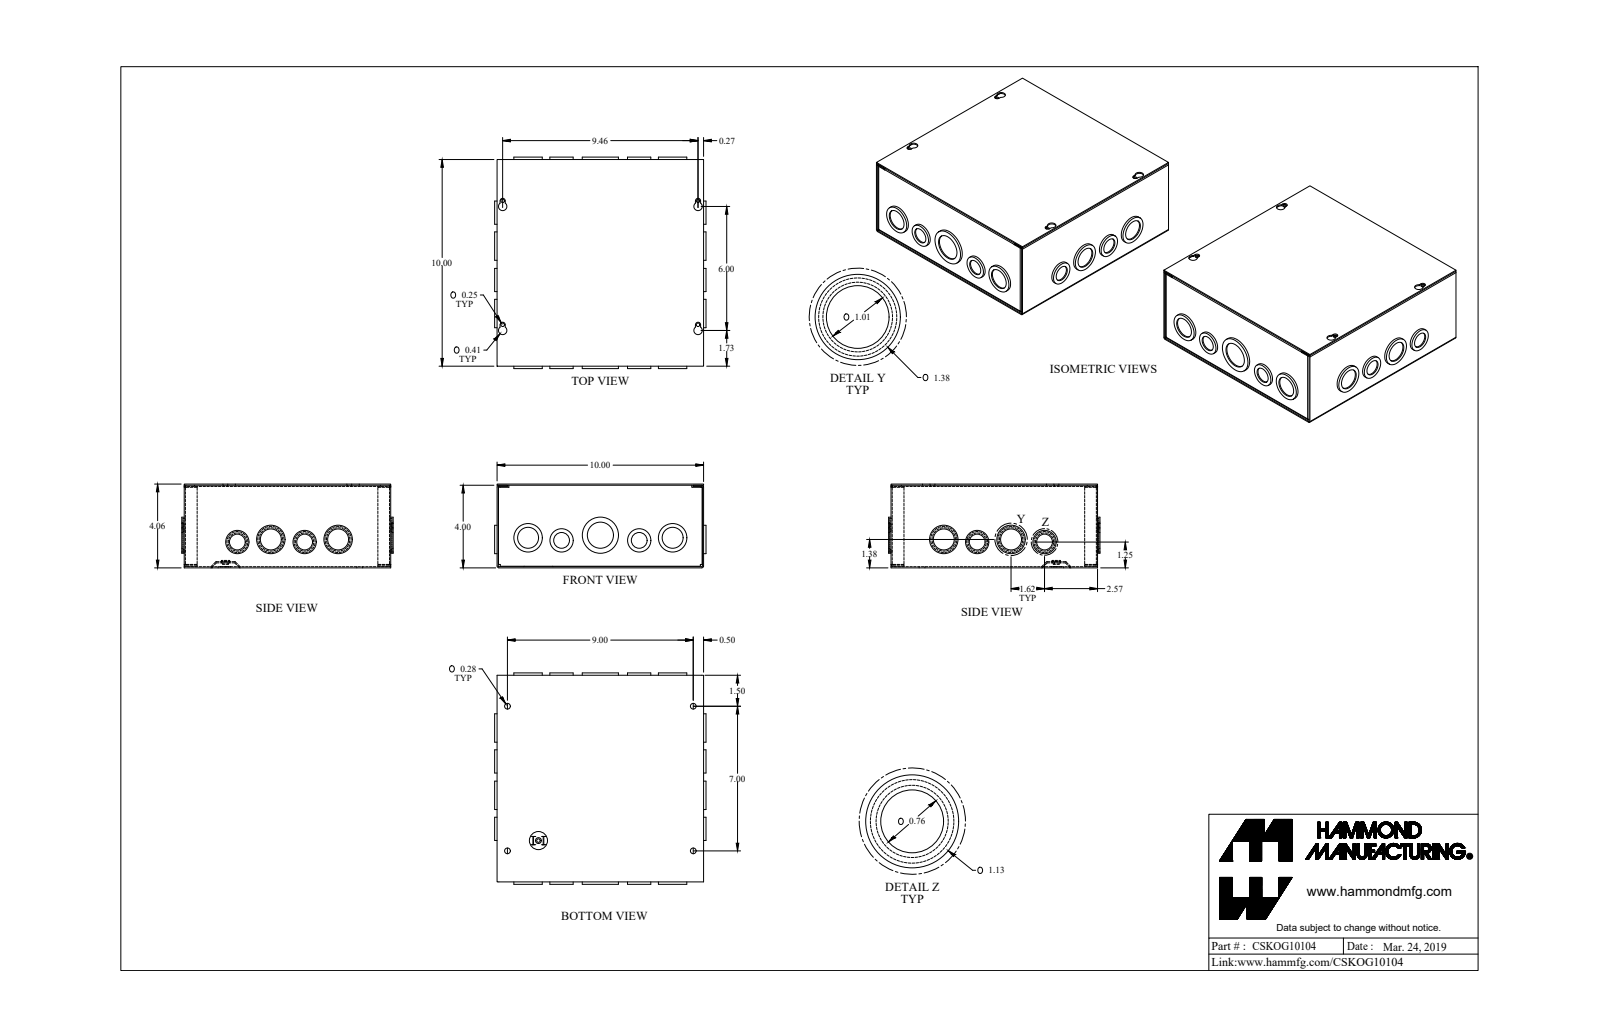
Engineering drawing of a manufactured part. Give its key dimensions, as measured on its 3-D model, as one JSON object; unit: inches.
{"part_name": "CSKOG10104_Default", "step_written_by": "SolidWorks 2019 (CONFIG_CONTROL_DESIGN)", "units": "inches", "bodies": {"solids": 4, "faces": 421, "planar": 197, "cylindrical": 216, "other": 8}, "overall_size": [10.234, 10.234, 4.057], "volume_in3": 22.85, "surface_area_in2": 811.7, "round_holes": [[1.011, 8], [1.261, 6], [0.17, 5], [0.281, 4], [0.761, 4], [0.5, 1], [1.636, 1]], "round_bosses_or_shafts": [[1.125, 6], [1.375, 5], [0.875, 4], [1.125, 2], [0.875, 2], [1.75, 1], [1.375, 1], [0.492, 1]], "partial_cylinders_radius": [[0.029, 12], [0.086, 12], [0.057, 8], [0.125, 4], [0.203, 4]], "face_to_face_distances": [0.057, 4, 9.943, 3.943, 4.057, 10, 9.886, 0.114, 0.08, 3.863], "hole_center_spacings": [1.625, 0.55, 6.504, 9.243, 11.289, 3.26, 7, 1.896]}
